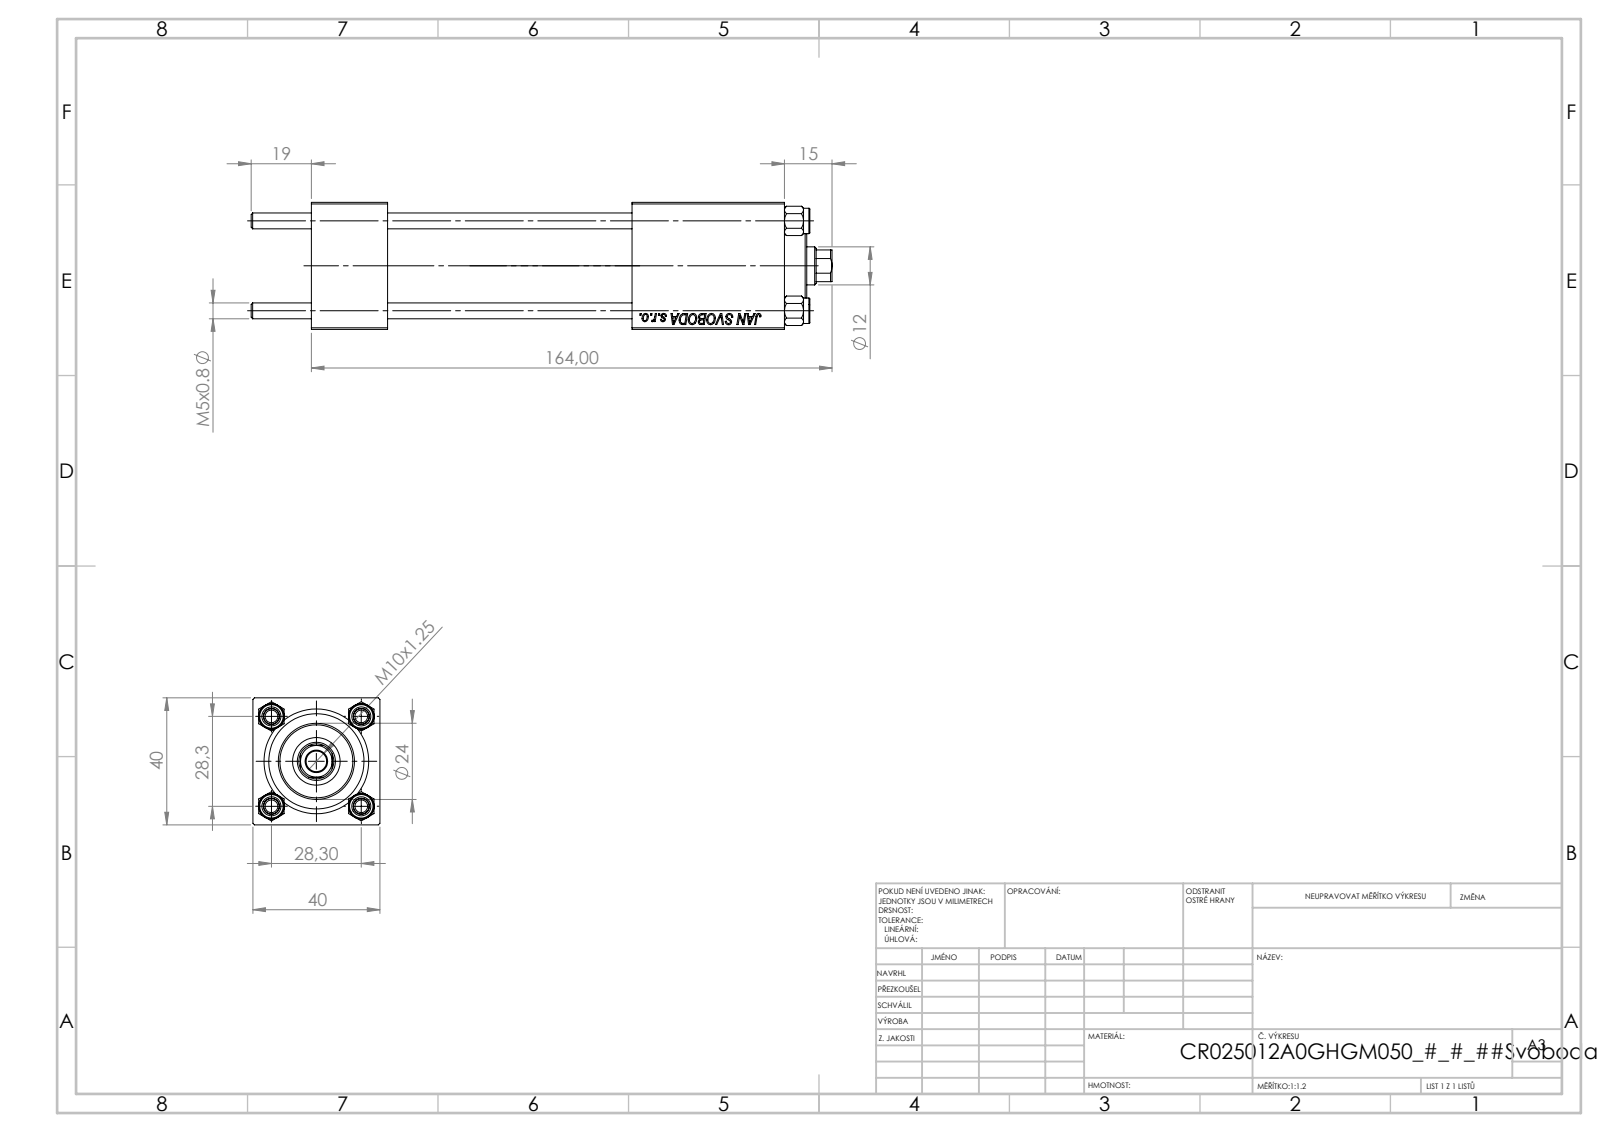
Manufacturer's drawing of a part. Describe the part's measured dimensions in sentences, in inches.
The part is named "V215_VC_A; V215CR_VCP; NUT_M5; CR025_012_A_0_G_A_G_M_020_+#_##_TYCINKA (+1 more)". Its 3-D file was written by "SolidWorks 2019 (CONFIG_CONTROL_DESIGN)". It is 11 solids with 1131 faces: 517 planar, 78 cylindrical and 536 other. Overall it measures 7.205 by 1.575 by 1.575 inches. Its volume is 9.672 cubic inches and its surface area 104.1 square inches. Round holes: 4 of diameter 0.197, 3 of diameter 0.787, 2 of diameter 0.276, 2 of diameter 0.518, 1 of diameter 0.256, 1 of diameter 0.472, 1 of diameter 0.591, 1 of diameter 0.984, 1 of diameter 1.181. Round bosses or shafts: 4 of diameter 0.315, 1 of diameter 1.22, 1 of diameter 0.945. Partial cylindrical surfaces (rounded edges, fillets, slot ends): 1 of radius 0.217. The main face-to-face distances are 1.575, 0.945, 5.866, 4.921, 4.736, 3.791, 1.13, 3.976, 3.031, 0.76. The hole center spacings are 0.788, 1.114, 1.576, 4.016.
